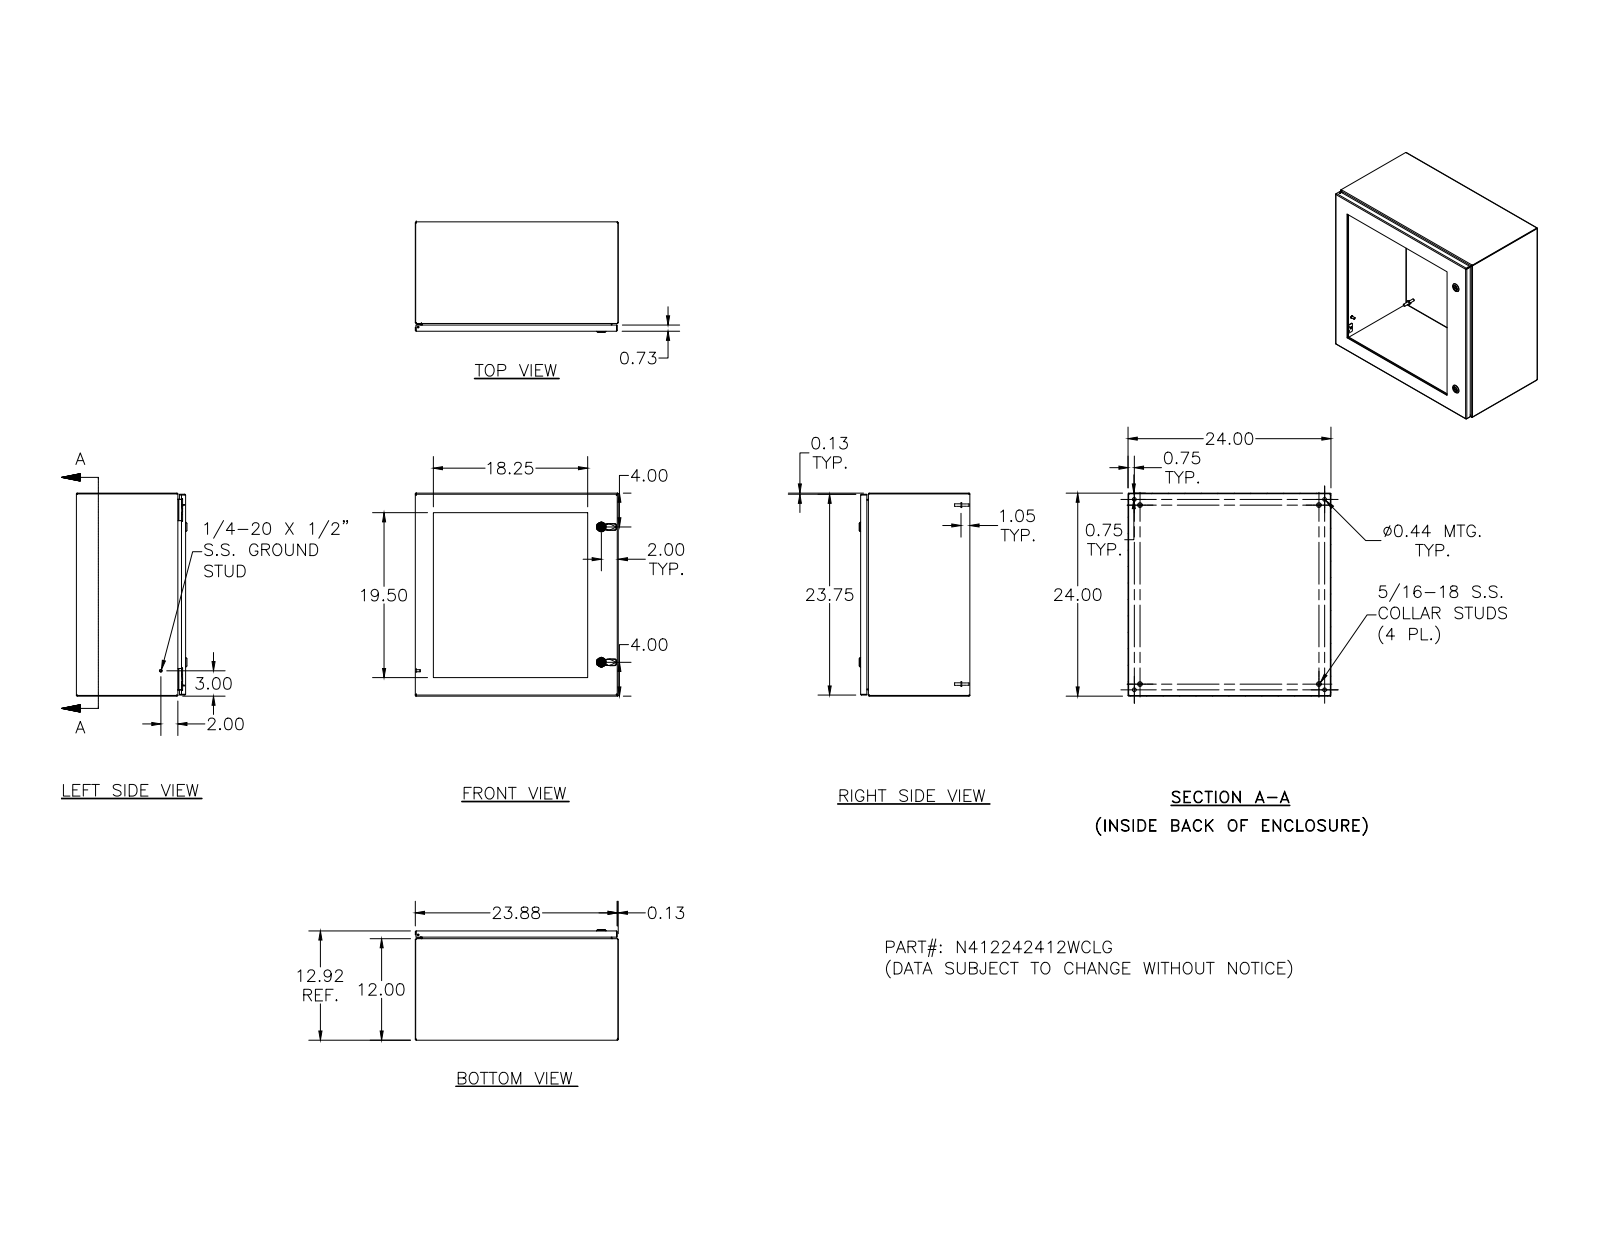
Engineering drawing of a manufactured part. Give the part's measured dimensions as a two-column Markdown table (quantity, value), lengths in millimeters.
| quantity | value |
| --- | --- |
| part name | N412242412WCLG |
| STEP written by | SolidWorks 2018 (AUTOMOTIVE_DESIGN) |
| units | millimeters |
| bodies | 84 solids, 2510 faces (971 planar, 762 cylindrical, 777 other) |
| overall size | 609.6 × 609.6 × 332.1 |
| volume | 4 331 000 mm³ |
| surface area | 3 436 000 mm² |
| round holes (diameter × count) | 4 × 22, 7.1 × 20, 4.8 × 5, 2.4 × 4, 3.9 × 4, 4.2 × 4, 4.4 × 4, 11.1 × 4, 5 × 2, 8 × 2, 10 × 2, 10.2 × 2 |
| round bosses / shafts (diameter × count) | 8.6 × 20, 4.8 × 20, 6.4 × 10, 14.3 × 4, 9.1 × 4, 8.1 × 4, 7.6 × 4, 7 × 4 |
| partial cylindrical surfaces (radius × count) | 0.3 × 54, 0.8 × 34, 1.3 × 26, 2.7 × 24, 0.5 × 23, 0.4 × 18, 3.2 × 16, 0.8 × 8 |
| main face-to-face distances | 1.9, 607.7, 326.2, 324.3, 605.8, 609.6, 6.4, 319.9, 318, 328.1 |
| hole center spacings | 101.6, 203.2, 536.8, 304.8, 508, 564.9, 527.1, 158 |
